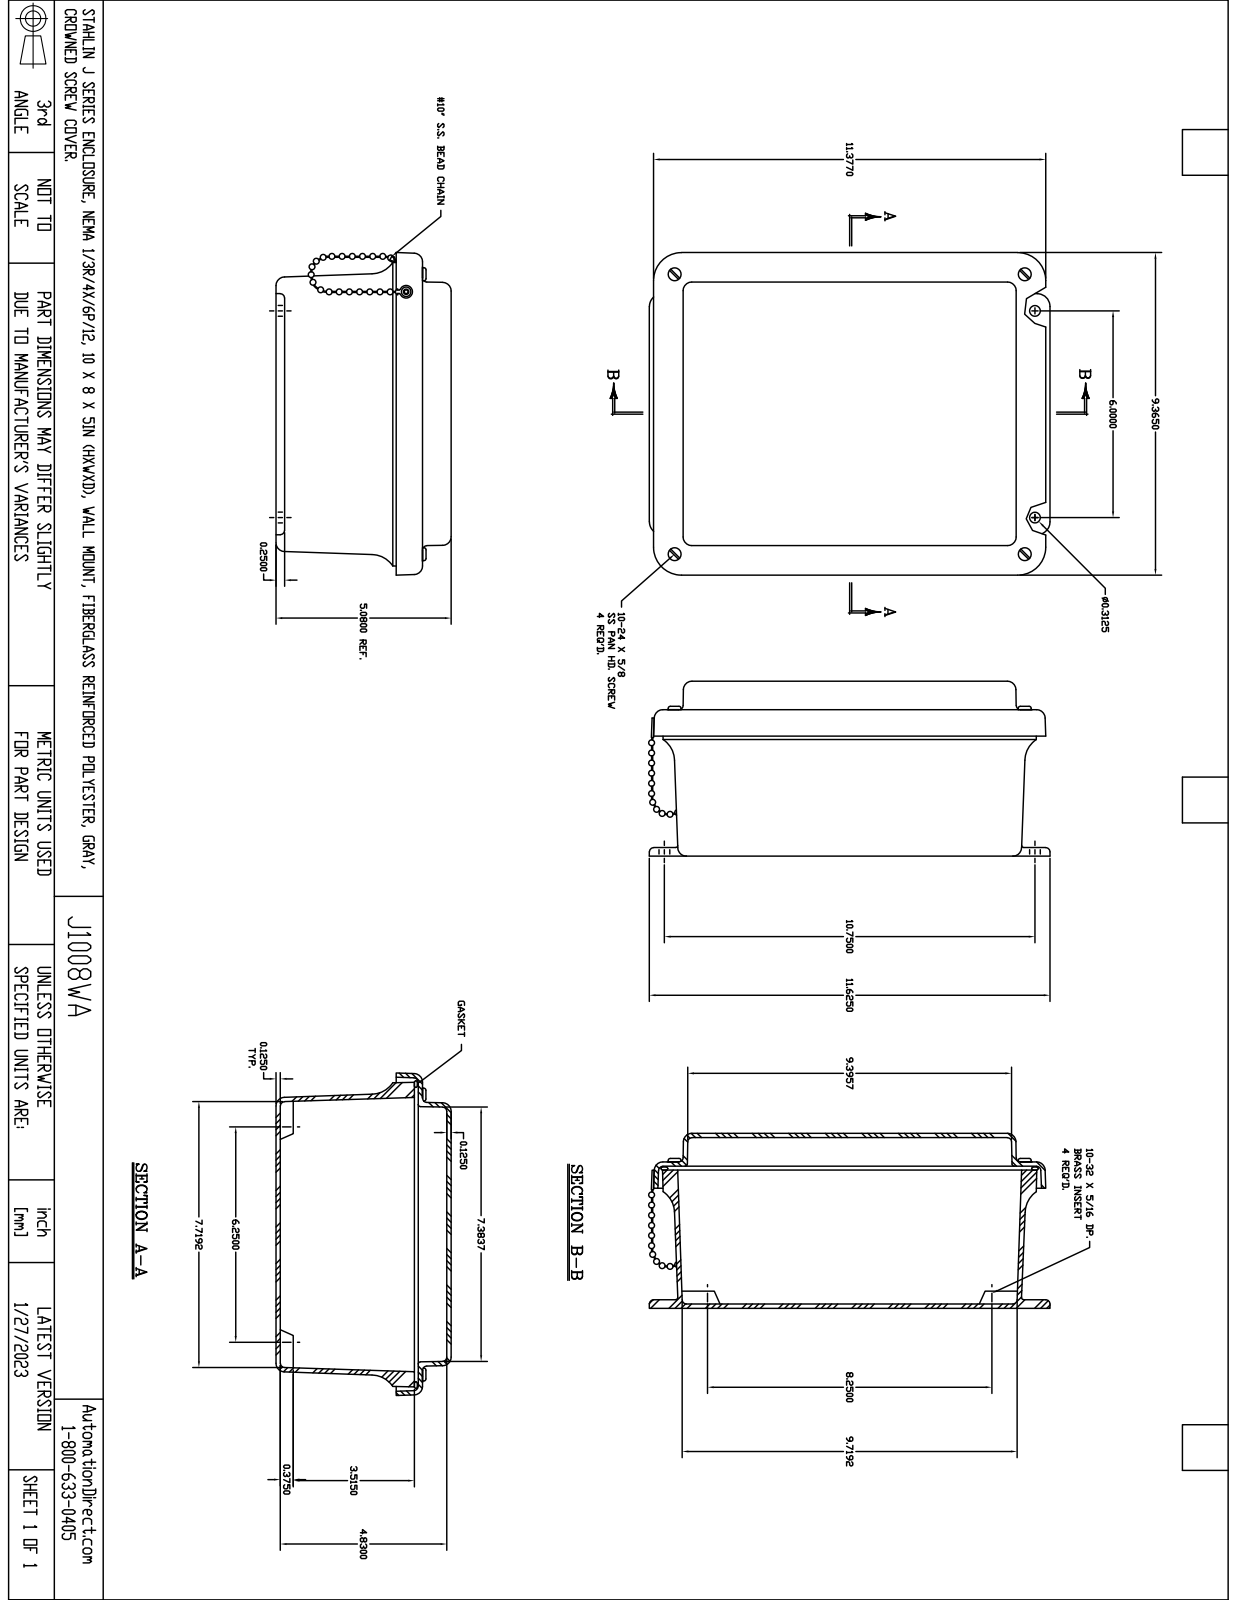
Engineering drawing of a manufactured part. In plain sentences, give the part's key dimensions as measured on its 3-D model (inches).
The part is named "M1008WA". Its 3-D file was written by "SolidWorks 2018 (AUTOMOTIVE_DESIGN)". It is 45 solids with 937 faces: 197 planar, 303 cylindrical and 437 other. Overall it measures 12.047 by 9.62 by 5.048 inches. Its volume is 61.67 cubic inches and its surface area 826.6 square inches. Round holes: 5 of diameter 0.14, 5 of diameter 0.152, 4 of diameter 0.145, 4 of diameter 0.156, 4 of diameter 0.218, 2 of diameter 0.187, 1 of diameter 0.126. Round bosses or shafts: 8 of diameter 0.27, 4 of diameter 0.19, 4 of diameter 0.156, 2 of diameter 0.375, 2 of diameter 0.25, 1 of diameter 0.283, 1 of diameter 0.125, 1 of diameter 0.125. Partial cylindrical surfaces (rounded edges, fillets, slot ends): 24 of radius 0.125, 20 of radius 0.031, 12 of radius 0.25, 8 of radius 0.2, 4 of radius 0.375, 4 of radius 0.75, 2 of radius 0.01, 2 of radius 0.063. The main face-to-face distances are 0.125, 0.125, 4.798, 4.923, 5.048, 4.924, 4.094, 0.829, 3.969, 0.954. The hole center spacings are 1.337, 2.5, 6, 6.25, 7.25, 7.251, 8.125, 8.25.
